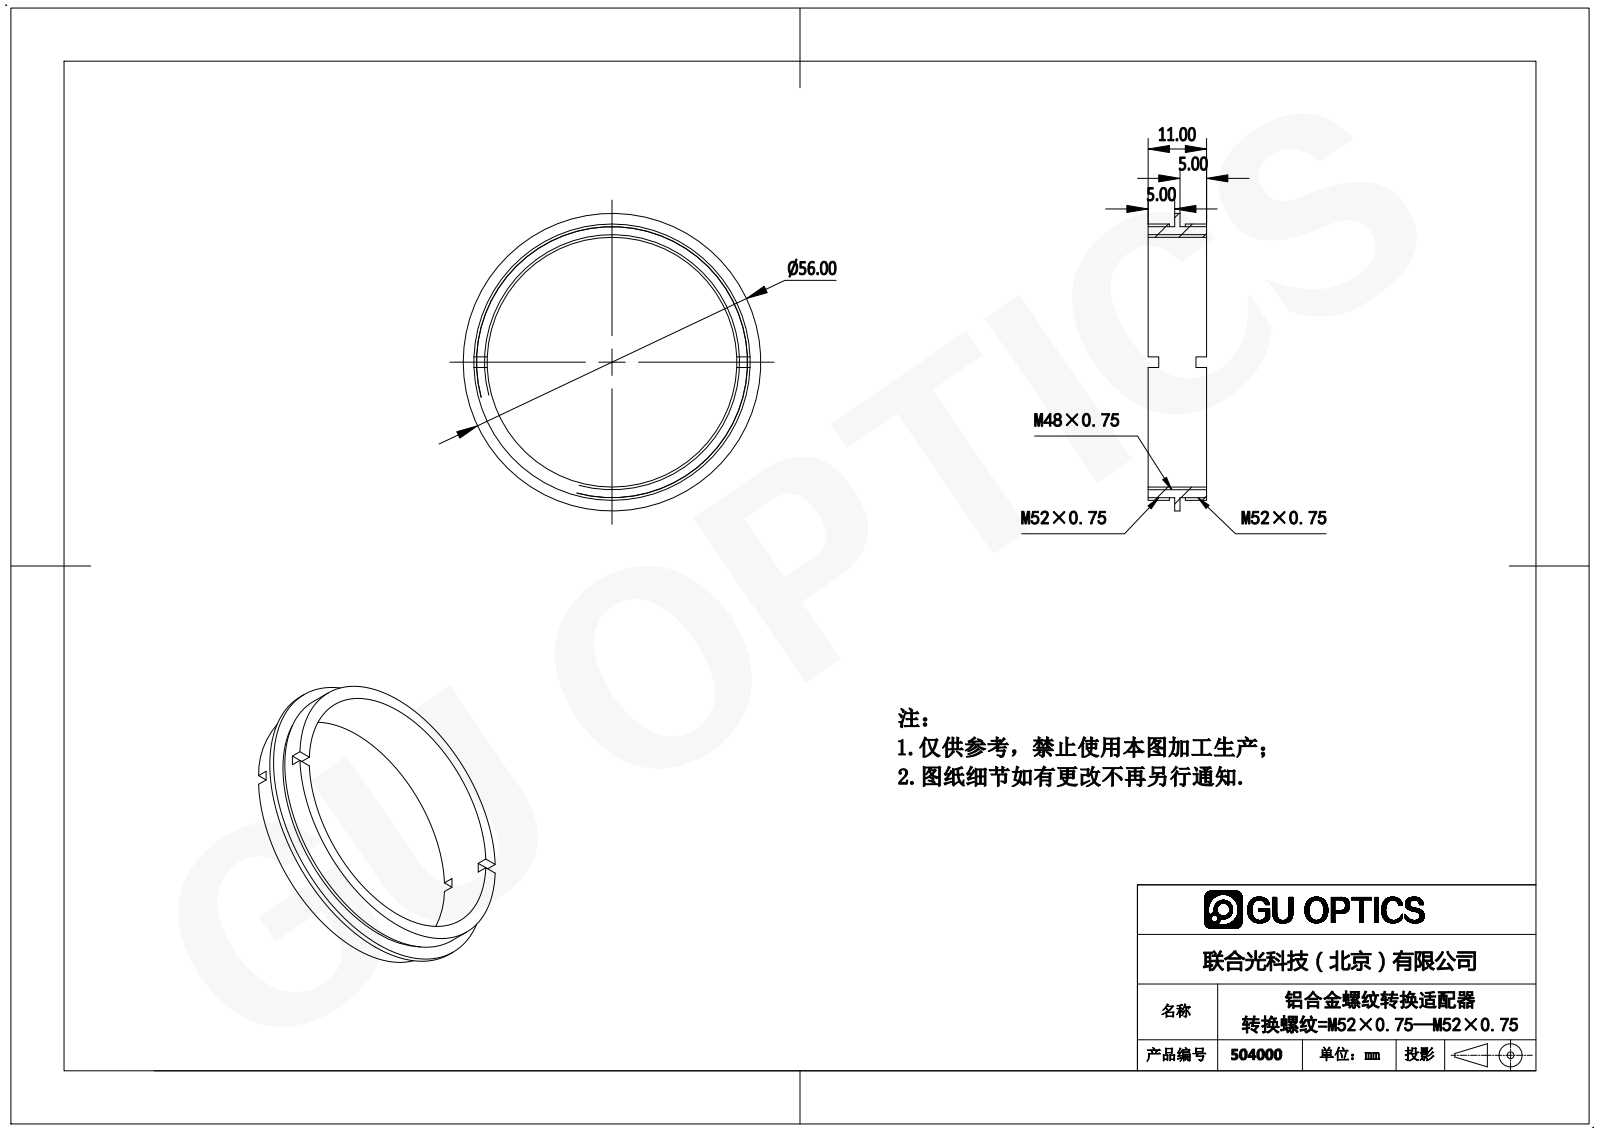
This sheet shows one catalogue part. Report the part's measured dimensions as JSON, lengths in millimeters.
{"part_name": "504000", "step_written_by": "SolidWorks 2016 (AUTOMOTIVE_DESIGN)", "units": "millimeters", "bodies": {"solids": 1, "faces": 32, "planar": 20, "cylindrical": 12, "other": 0}, "overall_size": [56, 56, 11], "volume_mm3": 4414, "surface_area_mm2": 5215, "round_holes": [[47, 1]], "round_bosses_or_shafts": [[56, 1], [52, 1], [51, 1]], "face_to_face_distances": [5, 6, 1, 11, 2, 4, 7, 3, 9]}
